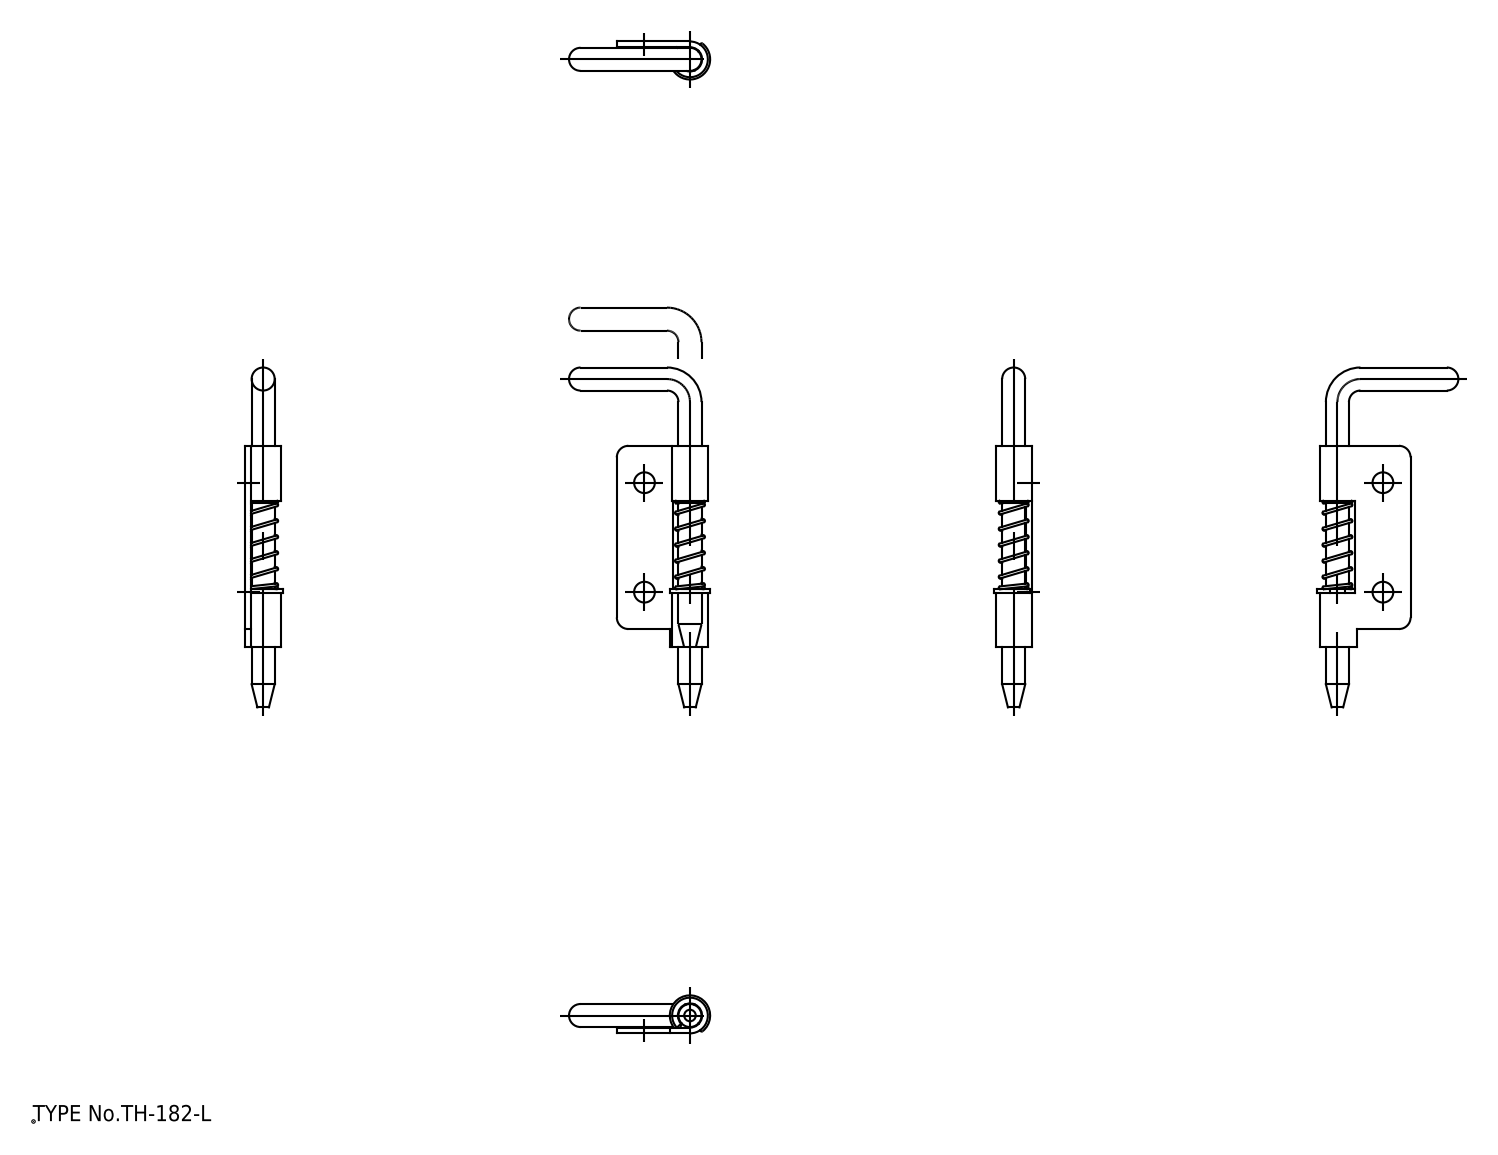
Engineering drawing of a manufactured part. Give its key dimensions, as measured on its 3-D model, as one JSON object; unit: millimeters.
{"part_name": "シャフト; ヒンジピース; スプリング_M2", "step_written_by": "spGate 19.8.4 (****-****-****-****) (AUTOMOTIVE_DESIGN)", "units": "millimeters", "bodies": {"solids": 3, "faces": 88, "planar": 27, "cylindrical": 27, "other": 34}, "overall_size": [59, 24.5, 6.6], "volume_mm3": 1571, "surface_area_mm2": 2580, "round_holes": [[3.6, 2], [4.2, 1]], "round_bosses_or_shafts": [[4, 2], [6.2, 1], [3.05, 1]], "partial_cylinders_radius": [[0.25, 6], [2, 2], [2.6, 1], [3.5, 1]], "face_to_face_distances": [1, 25.5, 9.5, 0.6, 24.9, 10.1, 35, 16, 15.4, 9.7], "hole_center_spacings": [19]}
